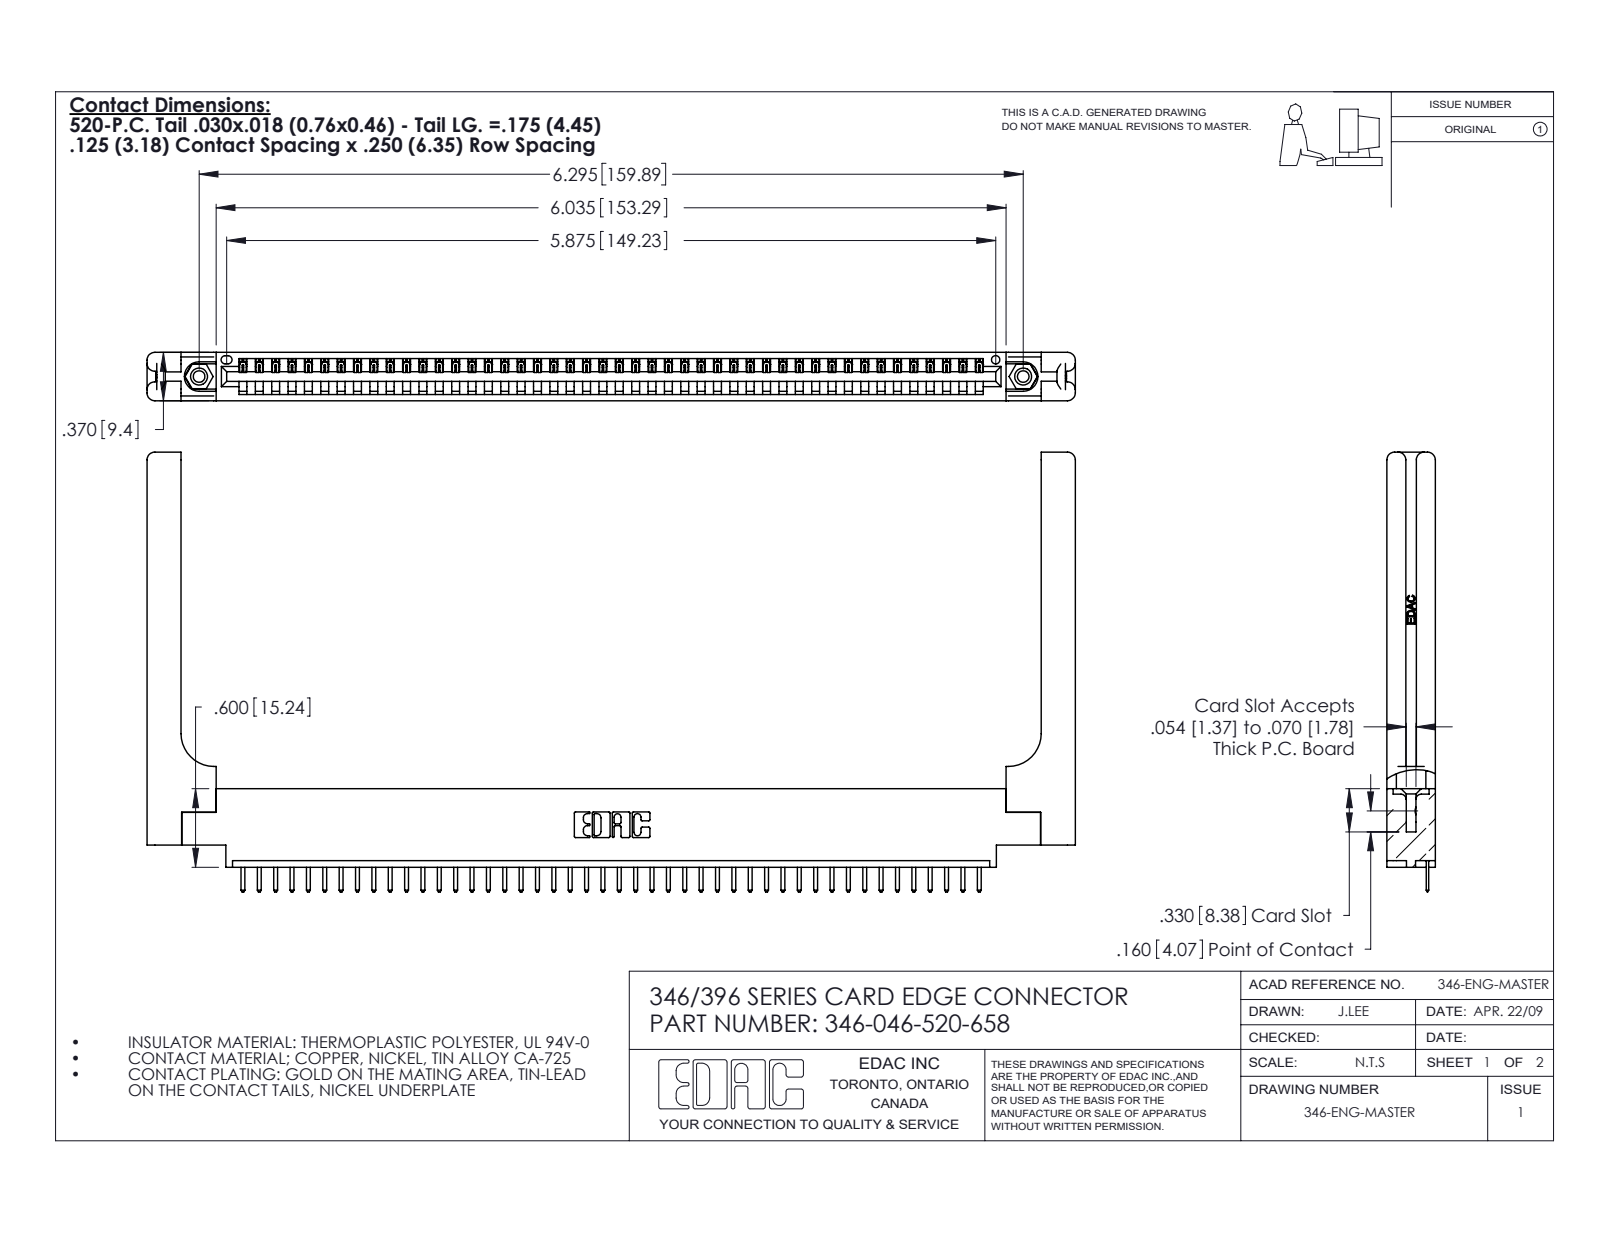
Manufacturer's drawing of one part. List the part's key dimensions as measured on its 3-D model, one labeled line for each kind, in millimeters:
Part name (STEP PRODUCT): 345-292-001_345-293-120; 345-250-001_345-250-001-102; 346 Part_0.170 Offset - 0.156 Dia-TH; 346-220-058_345-220-058 (+1 more)
STEP written by: SolidWorks 2020 (CONFIG_CONTROL_DESIGN)
Units: millimetres
Bodies: 51 solids, 3248 faces (2174 planar, 1014 cylindrical, 60 other)
Overall size (bounding box): 180.1 × 85.3 × 9.4
Volume: 24 480 mm³ · Surface area: 26 170 mm²
Round holes (diameter × count): ⌀2.3 ×2, ⌀3.2 ×2, ⌀4 ×2, ⌀1.6 ×1
Round bosses / shafts (diameter × count): ⌀3.9 ×2
Partial cylindrical surfaces — rounded edges, fillets, slot ends (radius × count): R0.3 ×94, R0.2 ×92, R0.3 ×22, R1.5 ×16, R0.2 ×6, R0.8 ×6, R0.7 ×3, R0.8 ×2
Main face-to-face distances: 9.4, 1.2, 8.2, 1.8, 3.8, 3.8, 6.4, 7.6, 0.6, 5.6
Hole centre spacings: 6.2, 154.6, 159.9
